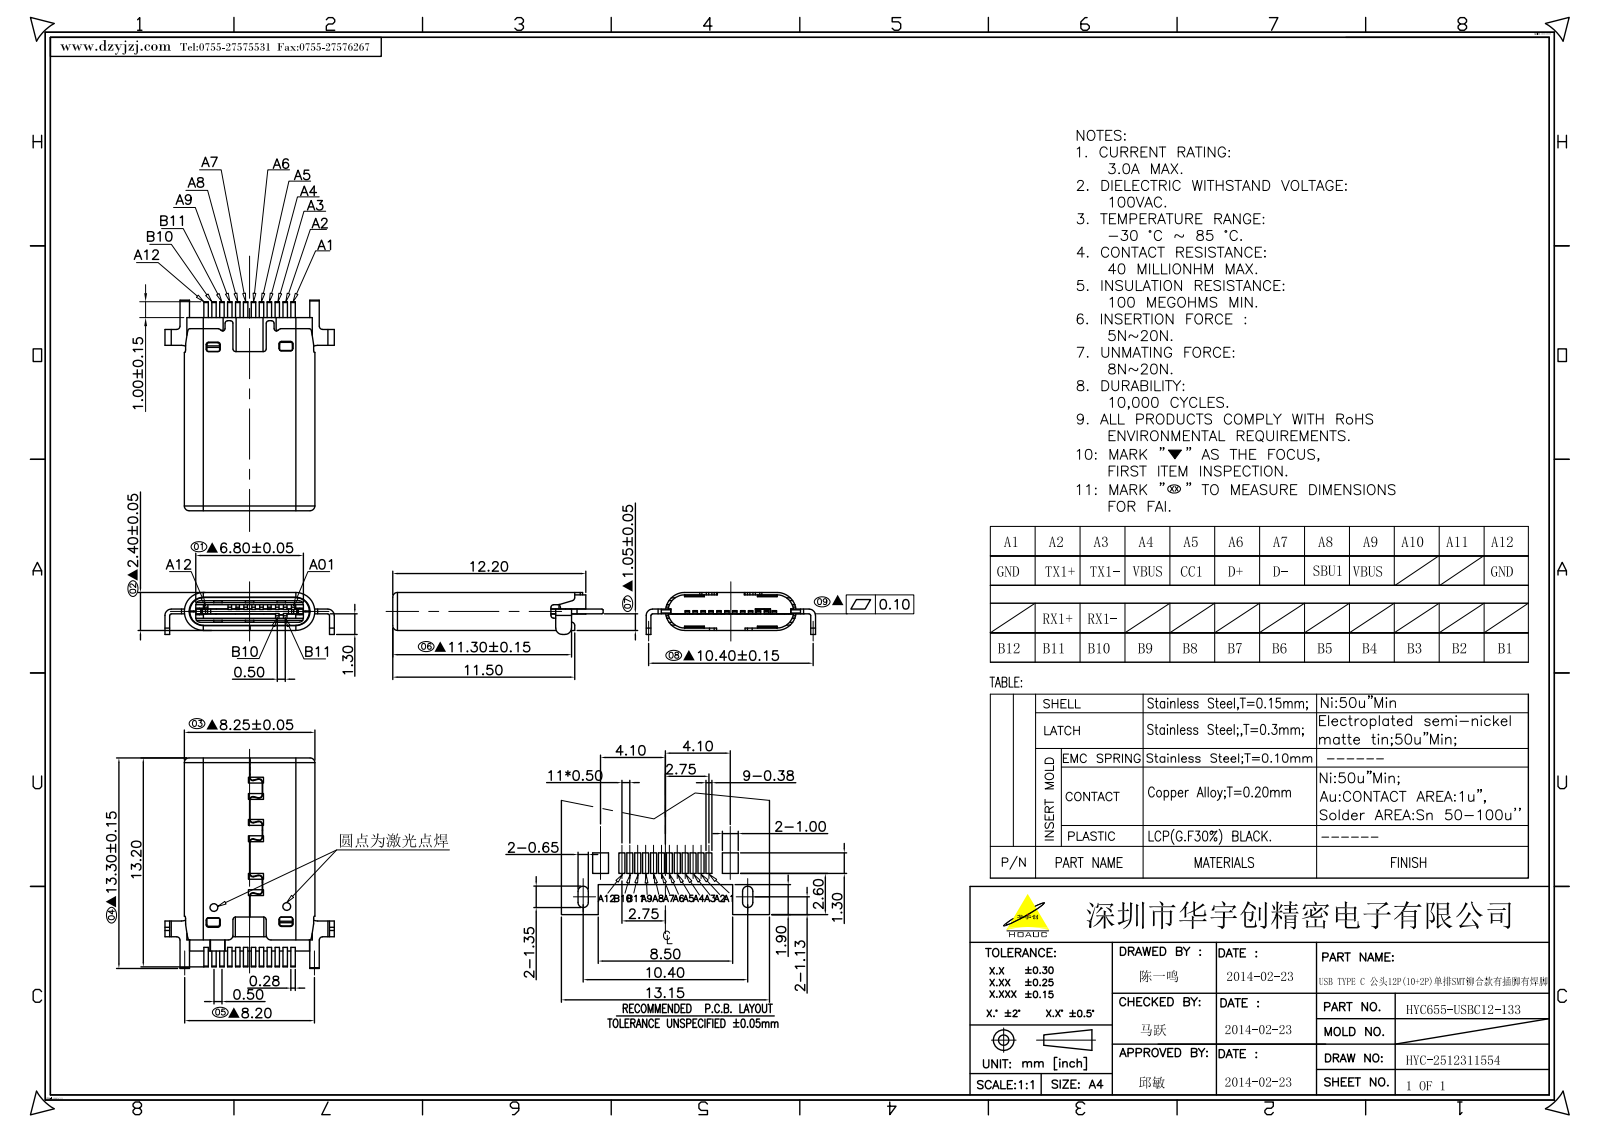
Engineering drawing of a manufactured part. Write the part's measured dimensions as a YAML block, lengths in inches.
part_name: "TANPIAN-PLASTIC_1_2__2"
step_written_by: "CREO PARAMETRIC BY PTC INC, 2022073 (AUTOMOTIVE_DESIGN)"
units: inches
bodies: {solids: 1, faces: 641, planar: 462, cylindrical: 173, other: 6}
overall_size: [0.524, 0.421, 0.104]
volume: 0.011
surface_area: 0.725
round_holes:
  - {diameter: 0.024, count: 2}
partial_cylinders:
  - {radius: 0.006, count: 38}
  - {radius: 0.005, count: 16}
  - {radius: 0.012, count: 13}
  - {radius: 0.004, count: 8}
  - {radius: 0.01, count: 6}
  - {radius: 0.008, count: 4}
  - {radius: 0.016, count: 4}
  - {radius: 0.007, count: 2}
face_to_face_distances: [0.031, 0.094, 0.063, 0.022, 0.041, 0.053, 0.02, 0.032, 0.073, 0.041]
hole_center_spacings: [0.181]
